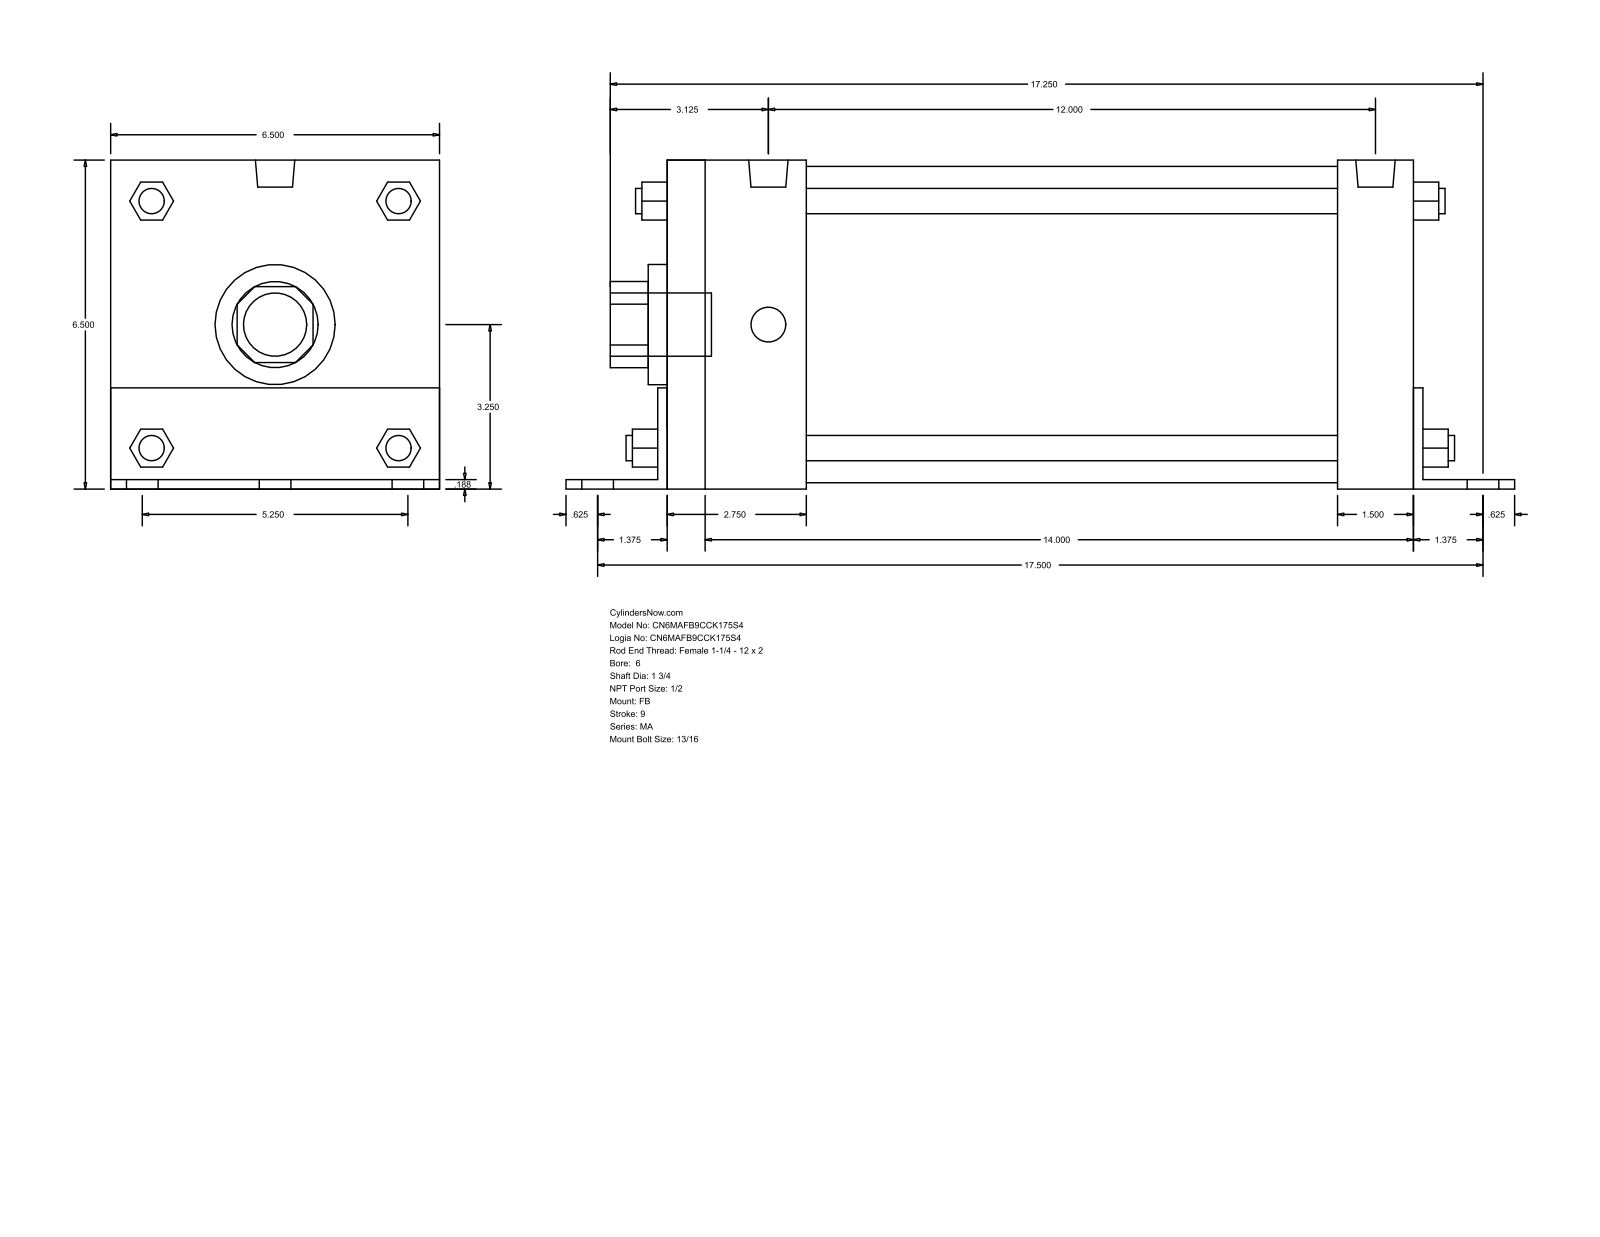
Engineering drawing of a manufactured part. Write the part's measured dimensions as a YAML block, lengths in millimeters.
part_name: "MA_FB__0600_1.75"
step_written_by: "GSSL Pune (CONFIG_CONTROL_DESIGN)"
units: millimeters
bodies: {solids: 0, faces: 140, planar: 105, cylindrical: 35, other: 0}
overall_size: [476.25, 165.15, 165.1]
round_holes:
  - {diameter: 44.45, count: 1}
  - {diameter: 60.33, count: 1}
  - {diameter: 158.75, count: 1}
round_bosses_or_shafts:
  - {diameter: 20.64, count: 6}
  - {diameter: 17.46, count: 4}
  - {diameter: 12.7, count: 4}
  - {diameter: 19.77, count: 2}
  - {diameter: 31.75, count: 1}
partial_cylinders:
  - {radius: 21.63, count: 1}
  - {radius: 32.05, count: 1}
face_to_face_distances: [165.1, 4.76, 374.66, 165.15, 379.42, 4.71, 160.39, 384.18, 38.11, 74.61]
